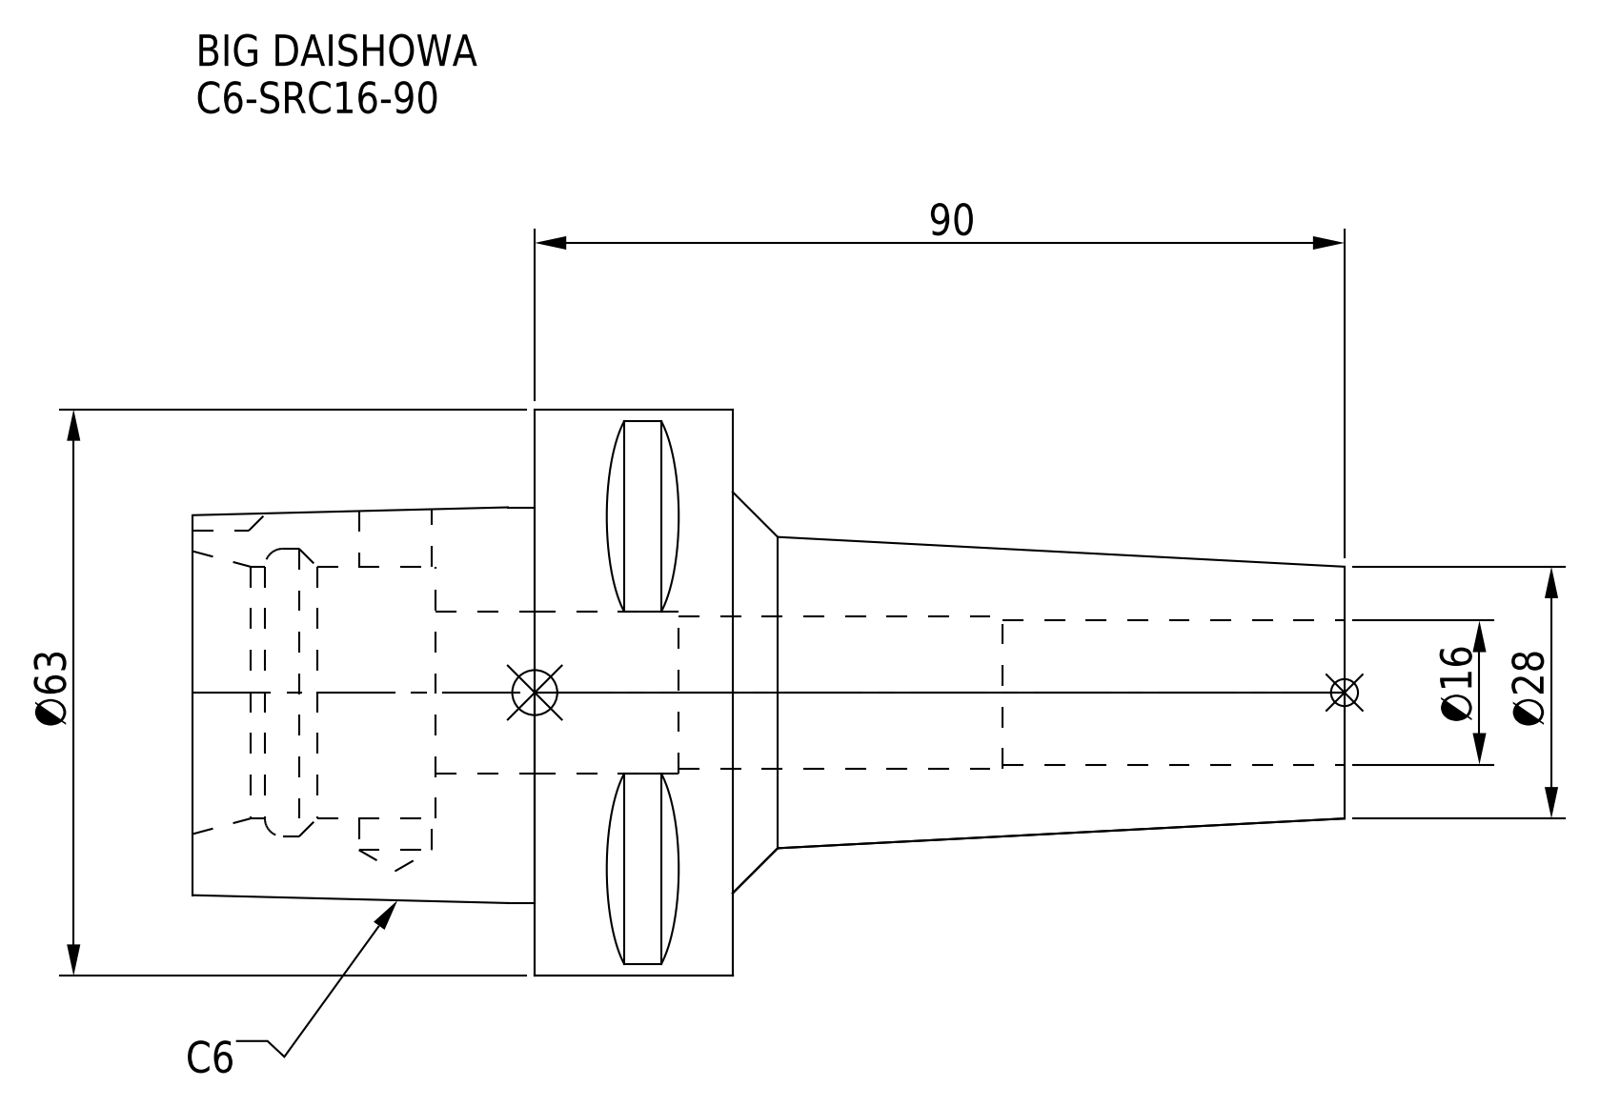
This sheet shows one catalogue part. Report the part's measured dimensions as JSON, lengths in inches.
{"part_name": "C6-SRC16-90", "step_written_by": "CREO PARAMETRIC BY PTC INC, 2016380 (AUTOMOTIVE_DESIGN)", "units": "inches", "bodies": {"solids": 1, "faces": 62, "planar": 29, "cylindrical": 19, "other": 14}, "overall_size": [5.039, 2.48, 2.48], "volume_in3": 8.276, "surface_area_in2": 46.06, "round_holes": [[0.319, 1], [0.63, 1], [0.669, 1], [0.709, 1], [1.102, 1], [1.26, 1]], "round_bosses_or_shafts": [[2.48, 1]], "partial_cylinders_radius": [[0.197, 1]], "face_to_face_distances": [0.866, 1.496, 2.362, 3.543, 2.677, 5.039, 1.063, 3.976, 1.299, 0.433]}
